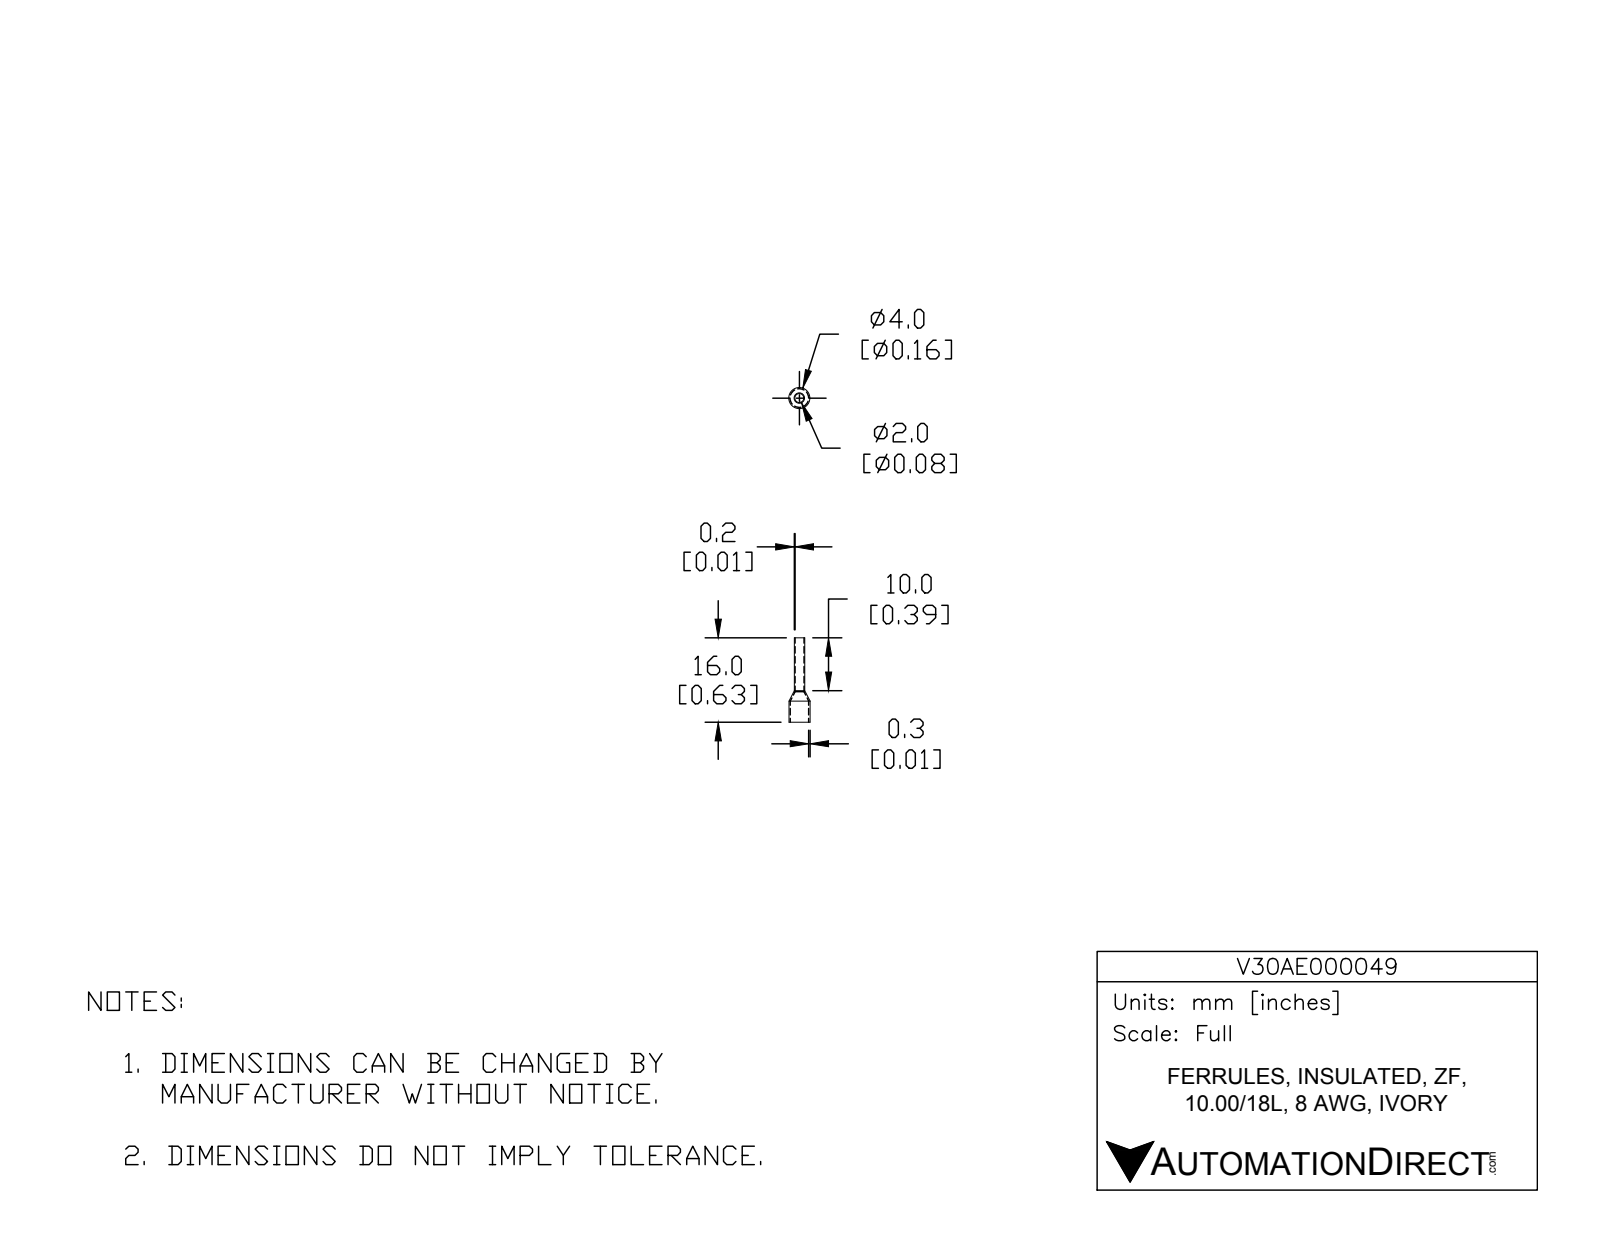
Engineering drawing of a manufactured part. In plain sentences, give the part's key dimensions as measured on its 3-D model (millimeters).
The part is named "V30AE000049". Its 3-D file was written by "SolidWorks 2017 (AUTOMOTIVE_DESIGN)". It is 1 solid with 14 faces: 2 planar, 8 cylindrical and 4 other. Overall it measures 16 by 4 by 4 millimeters. Its volume is 25 cubic millimeters and its surface area 253 square millimeters. Round holes: 1 of diameter 1.7, 1 of diameter 3.5. Round bosses or shafts: 1 of diameter 4, 1 of diameter 2. The main face-to-face distances are 16.
